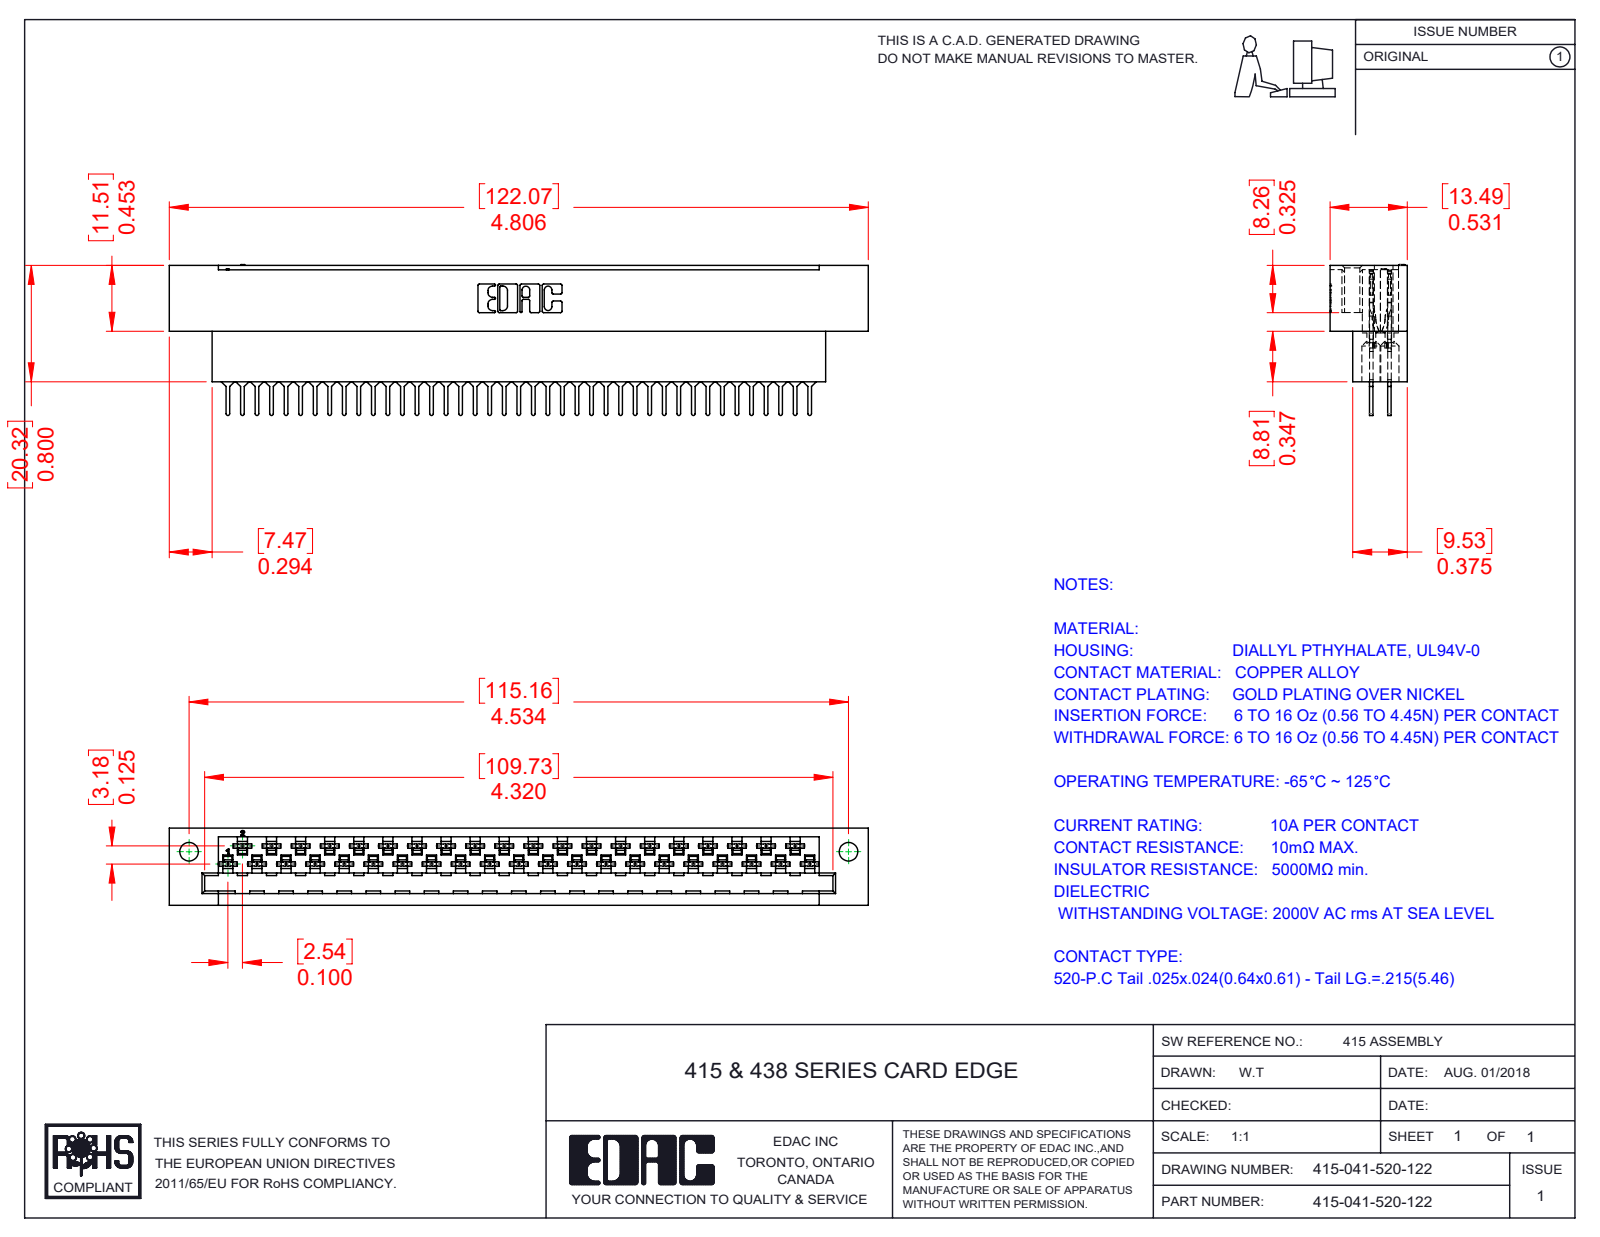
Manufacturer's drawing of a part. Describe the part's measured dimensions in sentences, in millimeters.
The part is named "415-041-520-122; 516-290-001_520; 415-210-001_415-210-041-122". Its 3-D file was written by "SolidWorks 2016 (CONFIG_CONTROL_DESIGN)". It is 42 solids with 4162 faces: 2661 planar, 1110 cylindrical and 391 other. Overall it measures 122.07 by 26.32 by 13.49 millimeters. Its volume is 19 962 cubic millimeters and its surface area 25 749 square millimeters. Round holes: 41 of diameter 1.27, 41 of diameter 3.3, 2 of diameter 3.25. Partial cylindrical surfaces (rounded edges, fillets, slot ends): 164 of radius 0.3, 164 of radius 0.56, 82 of radius 0.18, 82 of radius 0.2, 82 of radius 0.41, 82 of radius 2.03, 41 of radius 0.32, 22 of radius 0.25. The main face-to-face distances are 3.18, 0.61, 1.27, 1.88, 7.49, 13.49, 6.61, 6.88, 6, 6.71. The hole center spacings are 5.08, 10.16, 15.24, 20.32, 25.4, 30.48, 35.56, 2.54.
